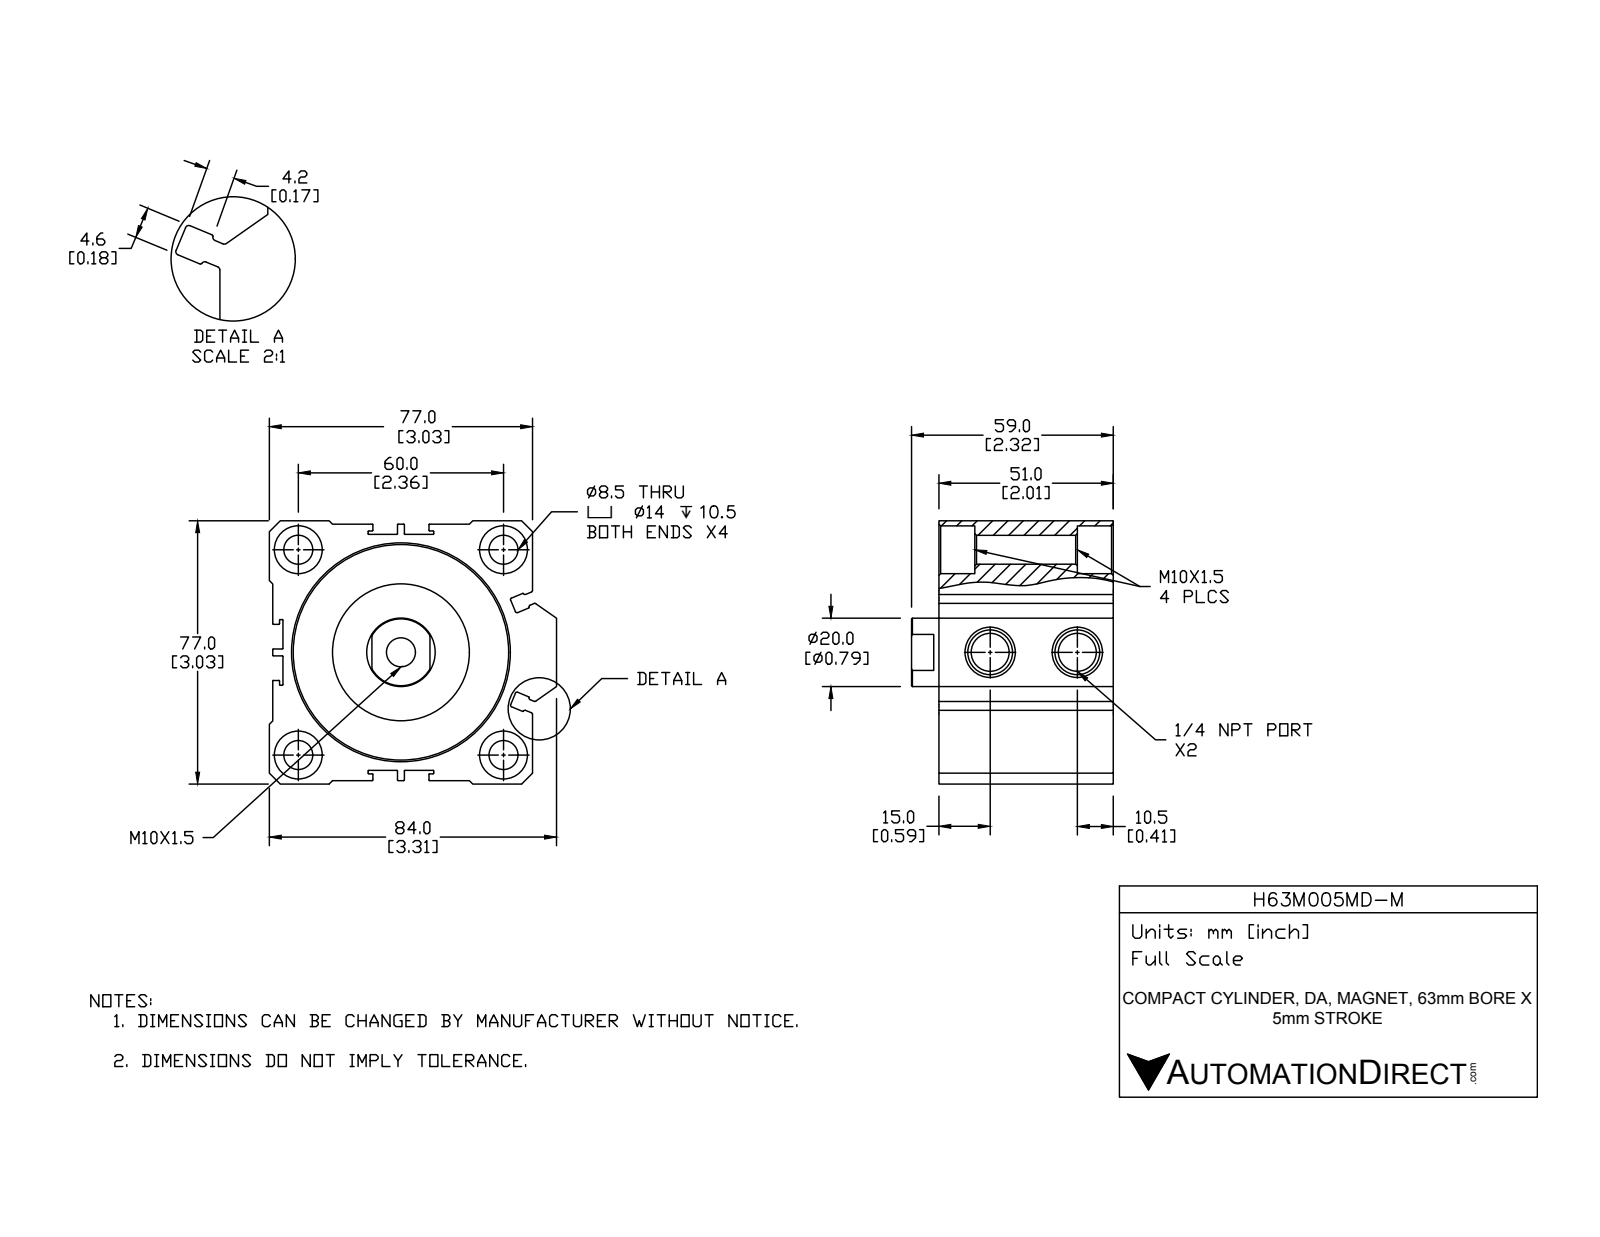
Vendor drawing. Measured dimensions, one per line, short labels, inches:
name: H63M005MD-M-BODY; H63M005MD-M-PISTON; H63M005MD-M
written by: SolidWorks 2015 (CONFIG_CONTROL_DESIGN)
unit: in
bodies: 2 solids, 255 faces (99 planar, 103 cylindrical, 53 other)
size: 3.307 × 3.031 × 2.323
volume: 14.65 in³; area: 102.1 in²
holes: 5× ⌀0.335, 4× ⌀0.551, 2× ⌀0.438, 1× ⌀0.787, 1× ⌀1.792, 1× ⌀2.48
bosses: 1× ⌀1.575, 1× ⌀1.535
rounds: 40× R0.008, 12× R0.02
face distances: 1.122, 0.217, 0.039, 2.992, 0.118, 0.906, 3.031, 0.157, 2.874, 1.339
hole spacings: 1.67, 2.362, 3.341, 1.004
